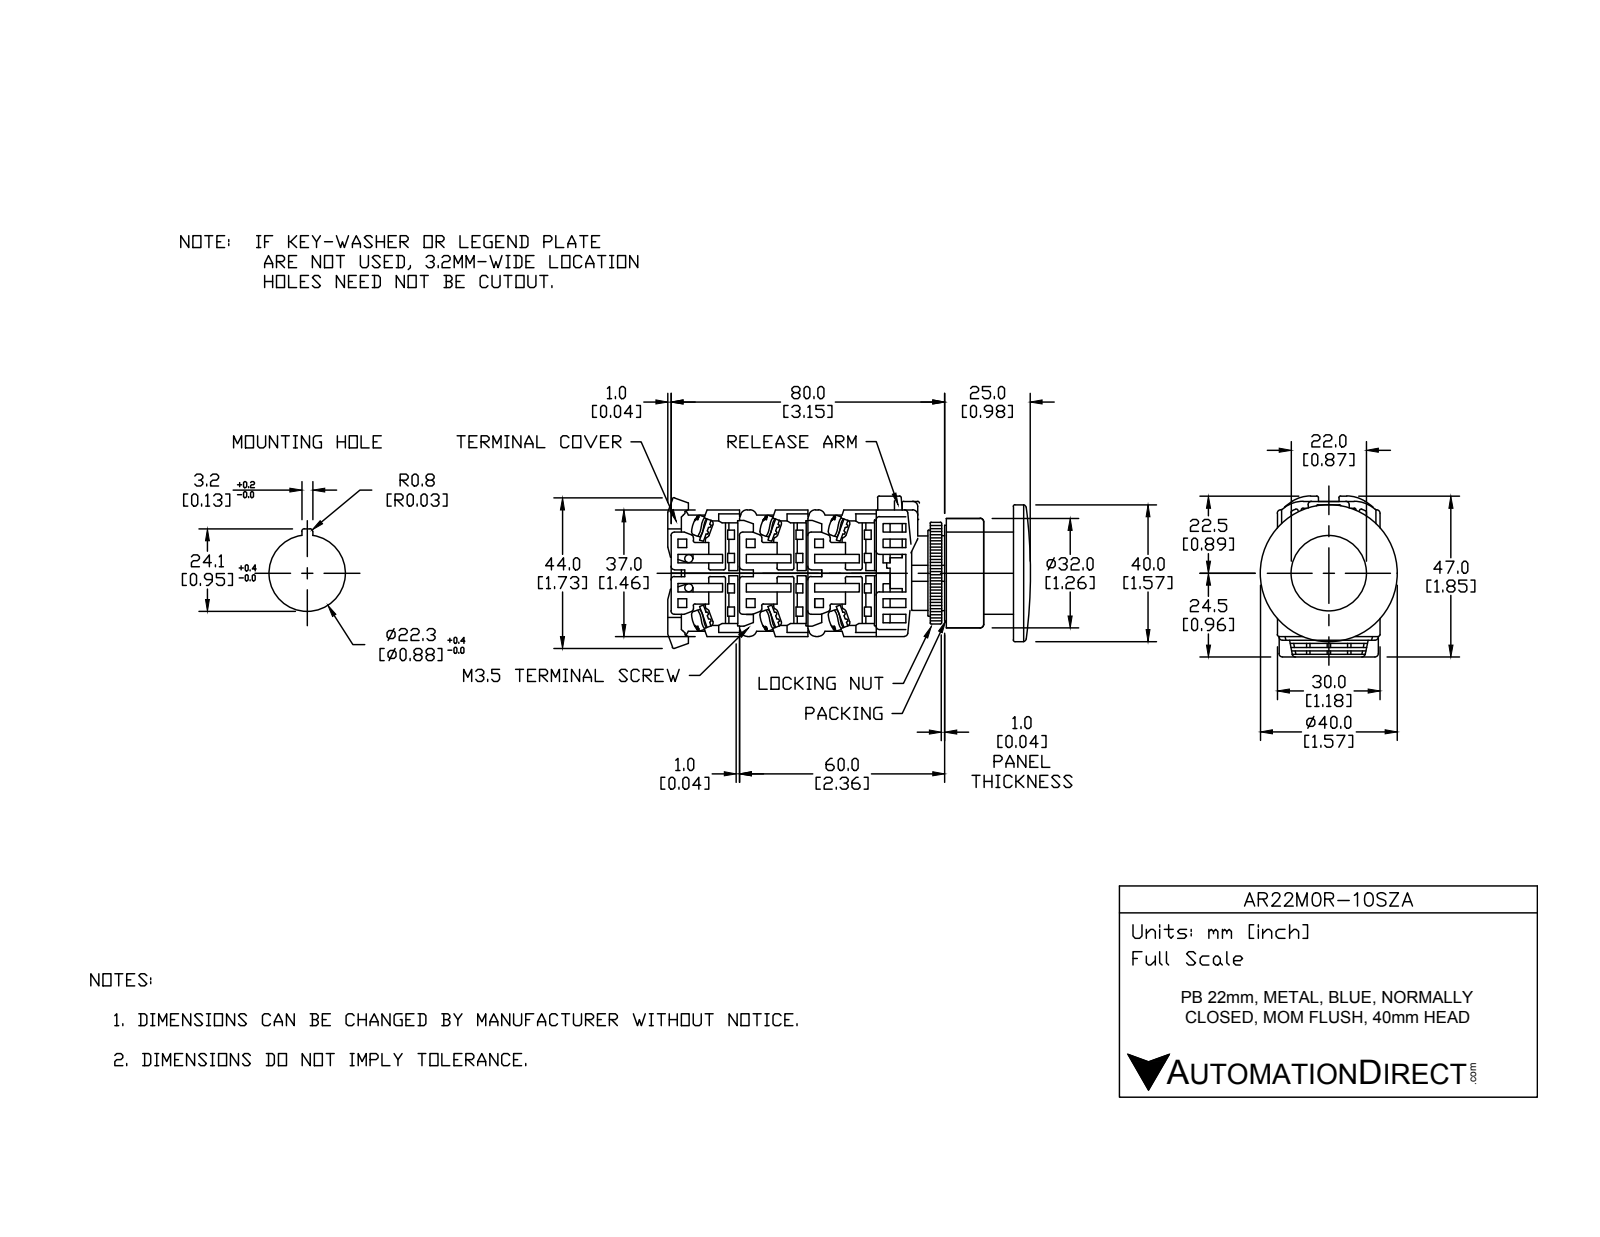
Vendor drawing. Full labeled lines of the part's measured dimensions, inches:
Part name (STEP PRODUCT): AR22M0R-10SZA
STEP written by: SolidWorks 2017 (AUTOMOTIVE_DESIGN)
Units: inches
Bodies: 12 solids, 304 faces (202 planar, 76 cylindrical, 26 other)
Overall size (bounding box): 2.539 × 1.693 × 1.575
Volume: 2.193 in³ · Surface area: 34.15 in²
Round holes (diameter × count): ⌀0.858 ×1, ⌀0.866 ×1, ⌀0.984 ×1, ⌀1.22 ×1
Round bosses / shafts (diameter × count): ⌀0.197 ×2, ⌀1.575 ×1, ⌀1.26 ×1, ⌀1.201 ×1, ⌀1.173 ×1, ⌀0.945 ×1, ⌀0.937 ×1, ⌀0.856 ×1
Partial cylindrical surfaces — rounded edges, fillets, slot ends (radius × count): R0.02 ×23, R0.069 ×4, R0.197 ×4, R0.157 ×2, R0.653 ×1, R0.693 ×1
Main face-to-face distances: 0.039, 0.394, 1.122, 0.709, 1.516, 0.827, 0.118, 0.079, 1.142, 0.295
